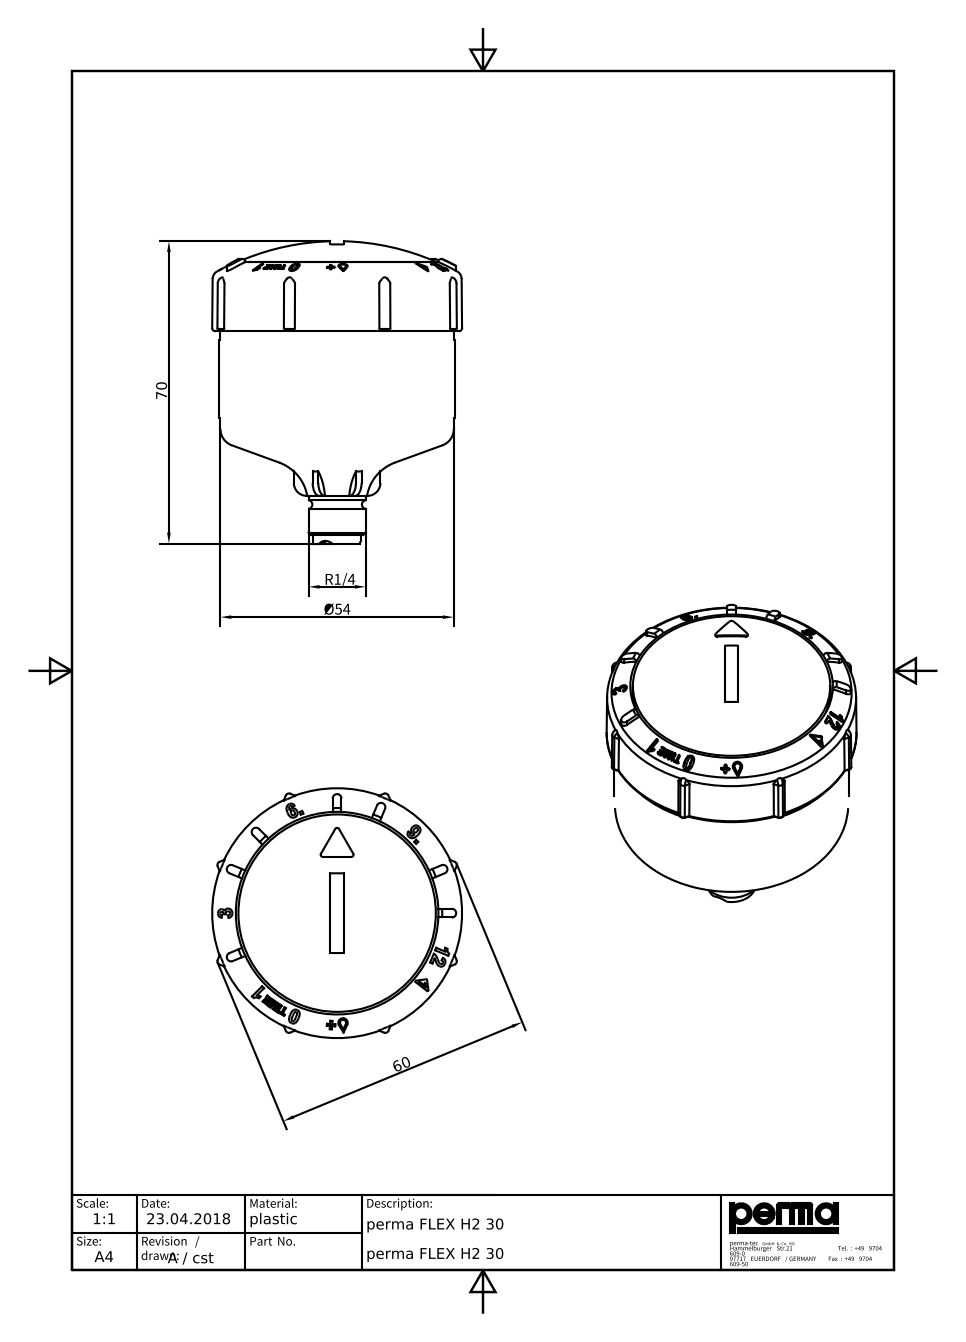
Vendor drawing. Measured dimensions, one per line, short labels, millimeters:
name: FLEX H2 30
written by: Autodesk Inventor 2018 (CONFIG_CONTROL_DESIGN)
unit: mm
bodies: 1 solid, 377 faces (153 planar, 44 cylindrical, 180 other)
size: 86.13 × 57.72 × 57.72
volume: 149 329 mm³; area: 16 297 mm²
holes: 1× ⌀46.8
bosses: 1× ⌀53.9, 1× ⌀45.6, 1× ⌀13.16, 1× ⌀11
rounds: 16× R0.3, 7× R1, 6× R3, 3× R0.2, 3× R0.5, 1× R0.7, 1× R1.08, 1× R20
face distances: 65.35, 1.5, 2, 3.1, 63.35, 20, 1.75, 9, 11, 65.76
